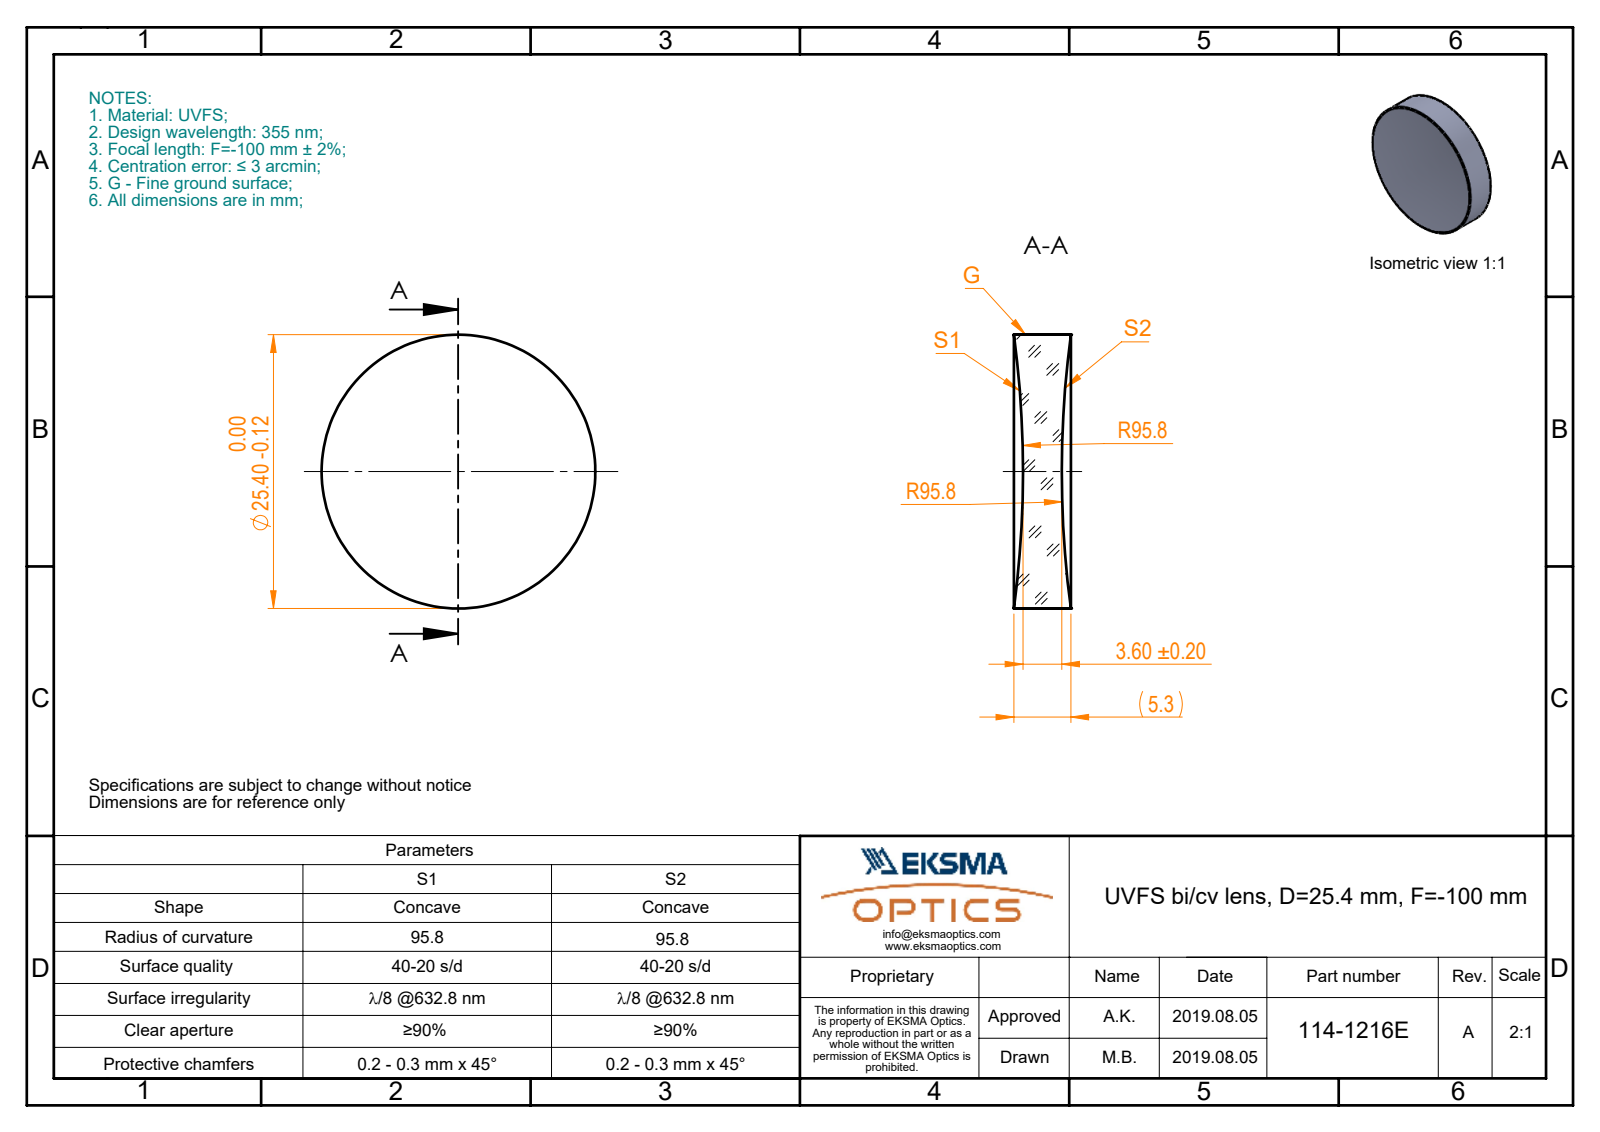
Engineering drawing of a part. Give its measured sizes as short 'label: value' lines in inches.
name: 114-1216E UVFS bi-cv 25.4 F-100
written by: SolidWorks 2017 (CONFIG_CONTROL_DESIGN)
unit: in
bodies: 1 solid, 6 faces (0 planar, 2 cylindrical, 4 other)
size: 1 × 1 × 0.208
volume: 0.137 in³; area: 2.232 in²
bosses: 1× ⌀1
